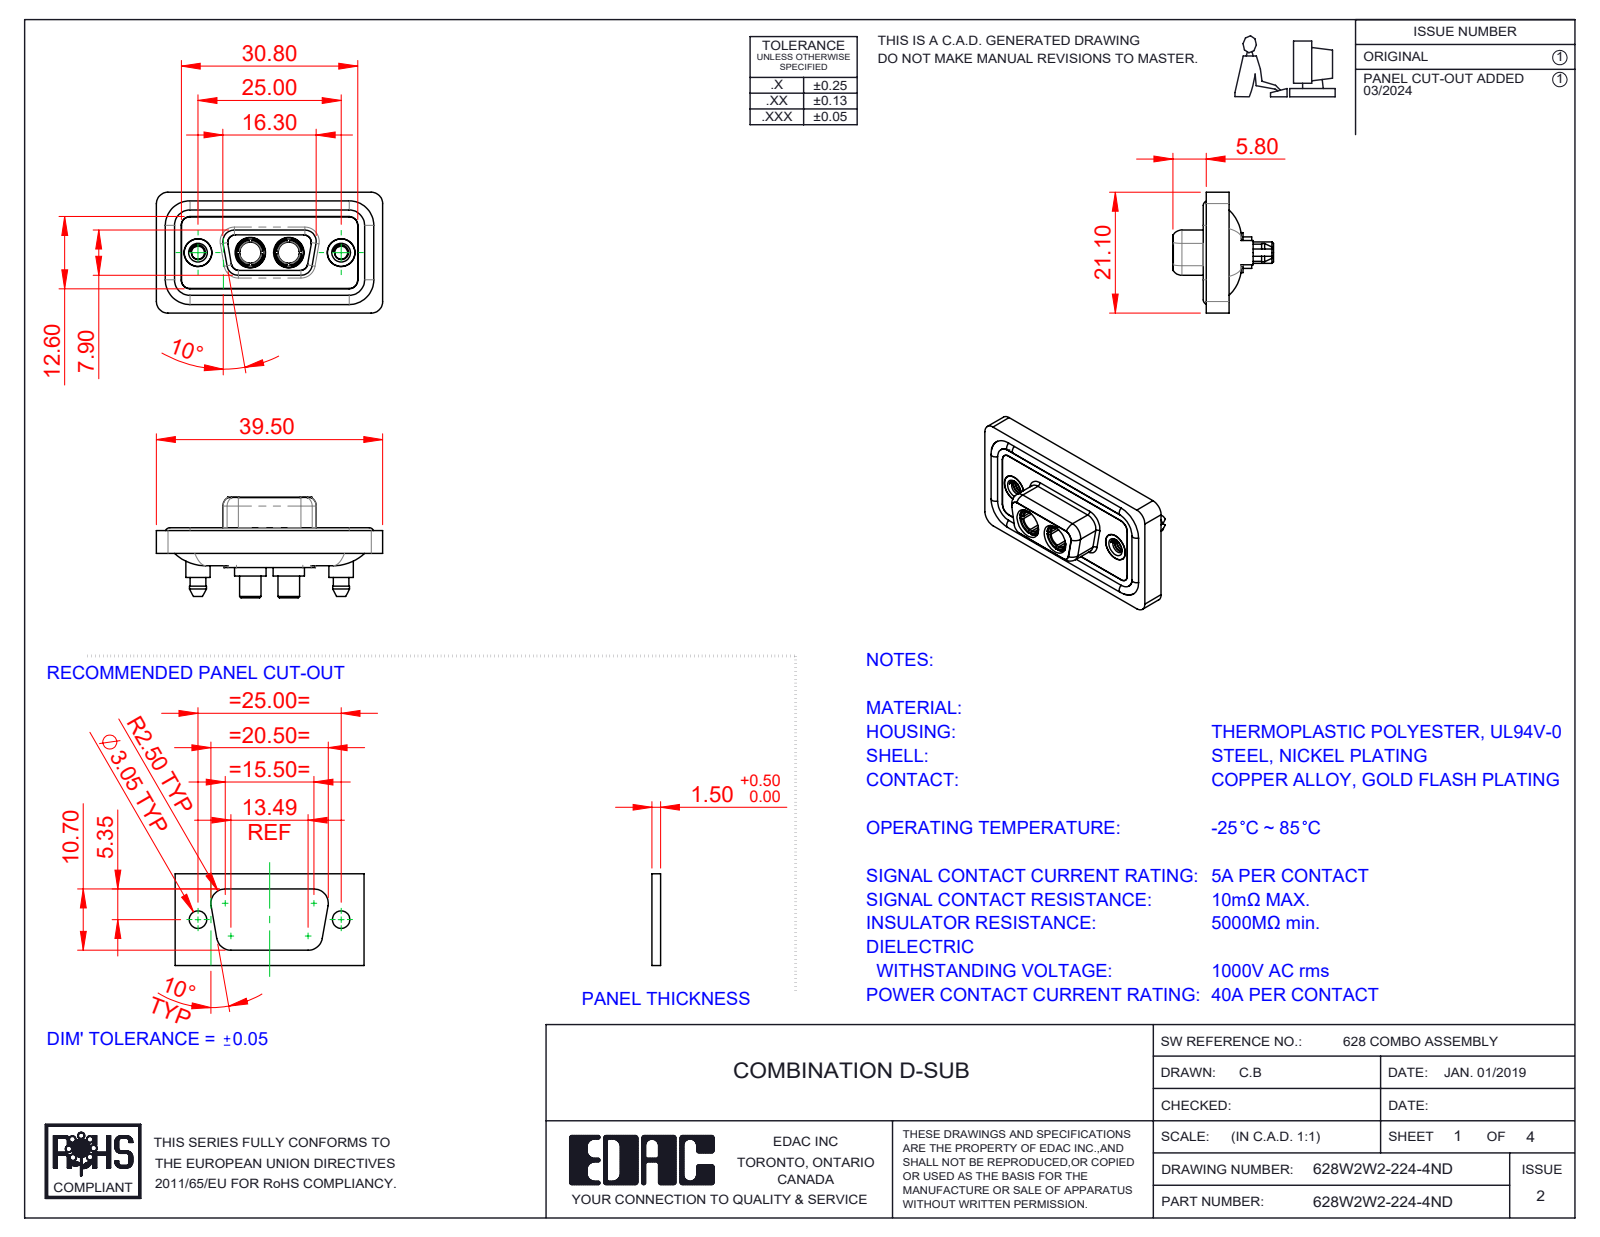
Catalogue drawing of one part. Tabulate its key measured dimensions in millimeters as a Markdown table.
| quantity | value |
| --- | --- |
| part name | 628Combo Shell Rear_09 Contacts; 628W2W2-224-4ND; 628Combo Threaded Boardlock_D; 628Combo Shell Front_09 Contacts (+3 more) |
| STEP written by | SolidWorks 2023 (CONFIG_CONTROL_DESIGN) |
| units | millimeters |
| bodies | 11 solids, 600 faces (179 planar, 282 cylindrical, 139 other) |
| overall size | 39.5 × 21.1 × 17.55 |
| volume | 4 885 mm³ |
| surface area | 7 997 mm² |
| round holes (diameter × count) | 4.85 × 4, 2.26 × 2, 3.7 × 2, 4 × 2, 4.05 × 2, 5 × 2, 5.3 × 2 |
| round bosses / shafts (diameter × count) | 1.6 × 4, 5.5 × 2, 5.4 × 2, 5.2 × 2, 4.96 × 2, 4.95 × 2, 4.8 × 2, 4.75 × 2 |
| partial cylindrical surfaces (radius × count) | 1.5 × 24, 2 × 18, 1.6 × 10, 1.35 × 8, 0.25 × 4, 0.5 × 4, 0.6 × 4, 0.65 × 4 |
| main face-to-face distances | 0.4, 1.8, 1.1, 2.9, 1.6, 0.5, 5.65, 7.45, 4, 1.5 |
| hole center spacings | 9.14, 15.86, 6.72, 25 |
